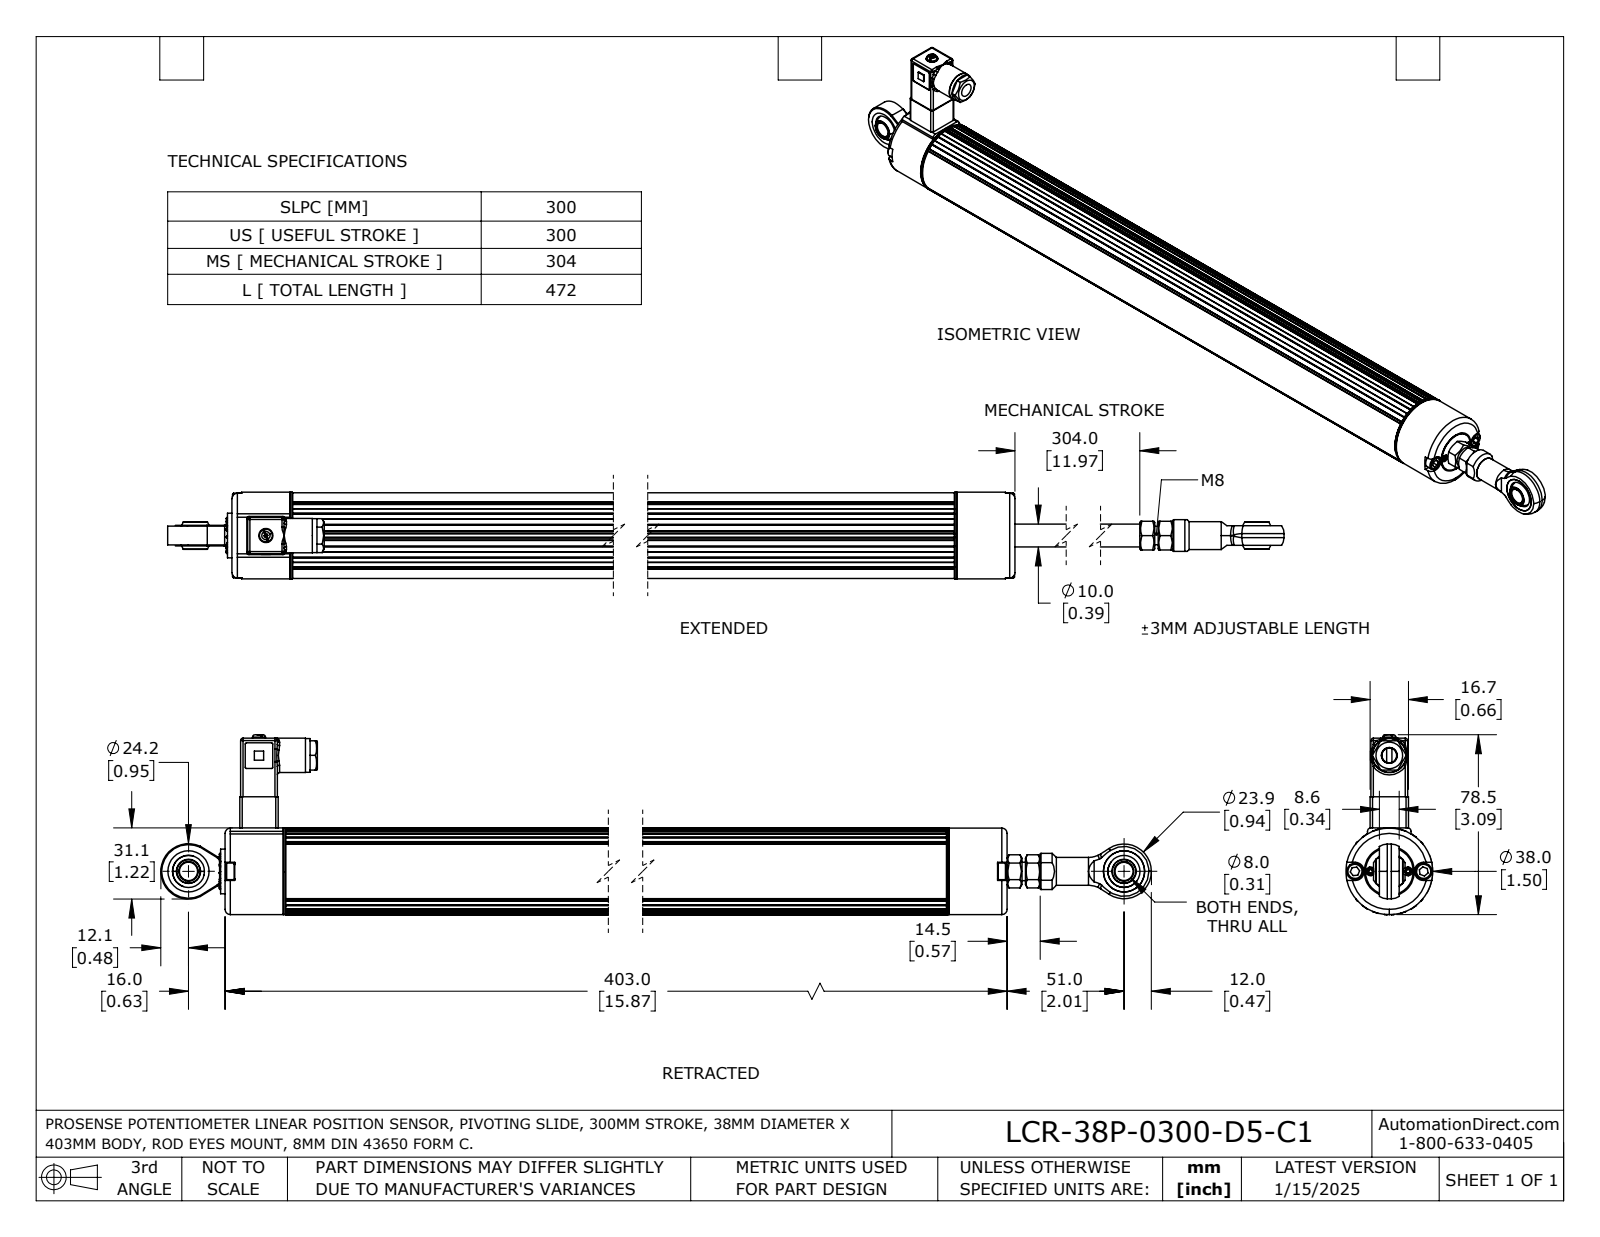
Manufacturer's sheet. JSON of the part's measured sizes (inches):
{"part_name": "LCR-38P-0300-D5-C1", "step_written_by": "SolidWorks 2023 (AUTOMOTIVE_DESIGN)", "units": "inches", "bodies": {"solids": 11, "faces": 657, "planar": 295, "cylindrical": 210, "other": 152}, "overall_size": [19.451, 3.093, 1.488], "volume_in3": 28.29, "surface_area_in2": 131.2, "round_holes": [[0.102, 6], [0.091, 4], [0.315, 3], [0.551, 3], [0.094, 2], [0.1, 2], [0.111, 2], [0.134, 2], [0.152, 2], [0.165, 2], [0.079, 1], [0.118, 1]], "round_bosses_or_shafts": [[0.063, 6], [0.283, 4], [0.15, 4], [0.48, 2], [0.079, 2], [1.488, 1], [0.823, 1], [0.768, 1]], "partial_cylinders_radius": [[0.008, 32], [0.039, 20], [0.02, 12], [0.016, 6], [0.012, 2], [0.059, 2], [0.083, 2], [0.098, 2]], "face_to_face_distances": [13.78, 1.043, 14.823, 0.031, 0.045, 0.612, 0.598, 0.014, 0.644, 0.138], "hole_center_spacings": [0.632, 0.075, 0.634, 0.264, 0.268, 0.285, 0.323, 0.394]}
